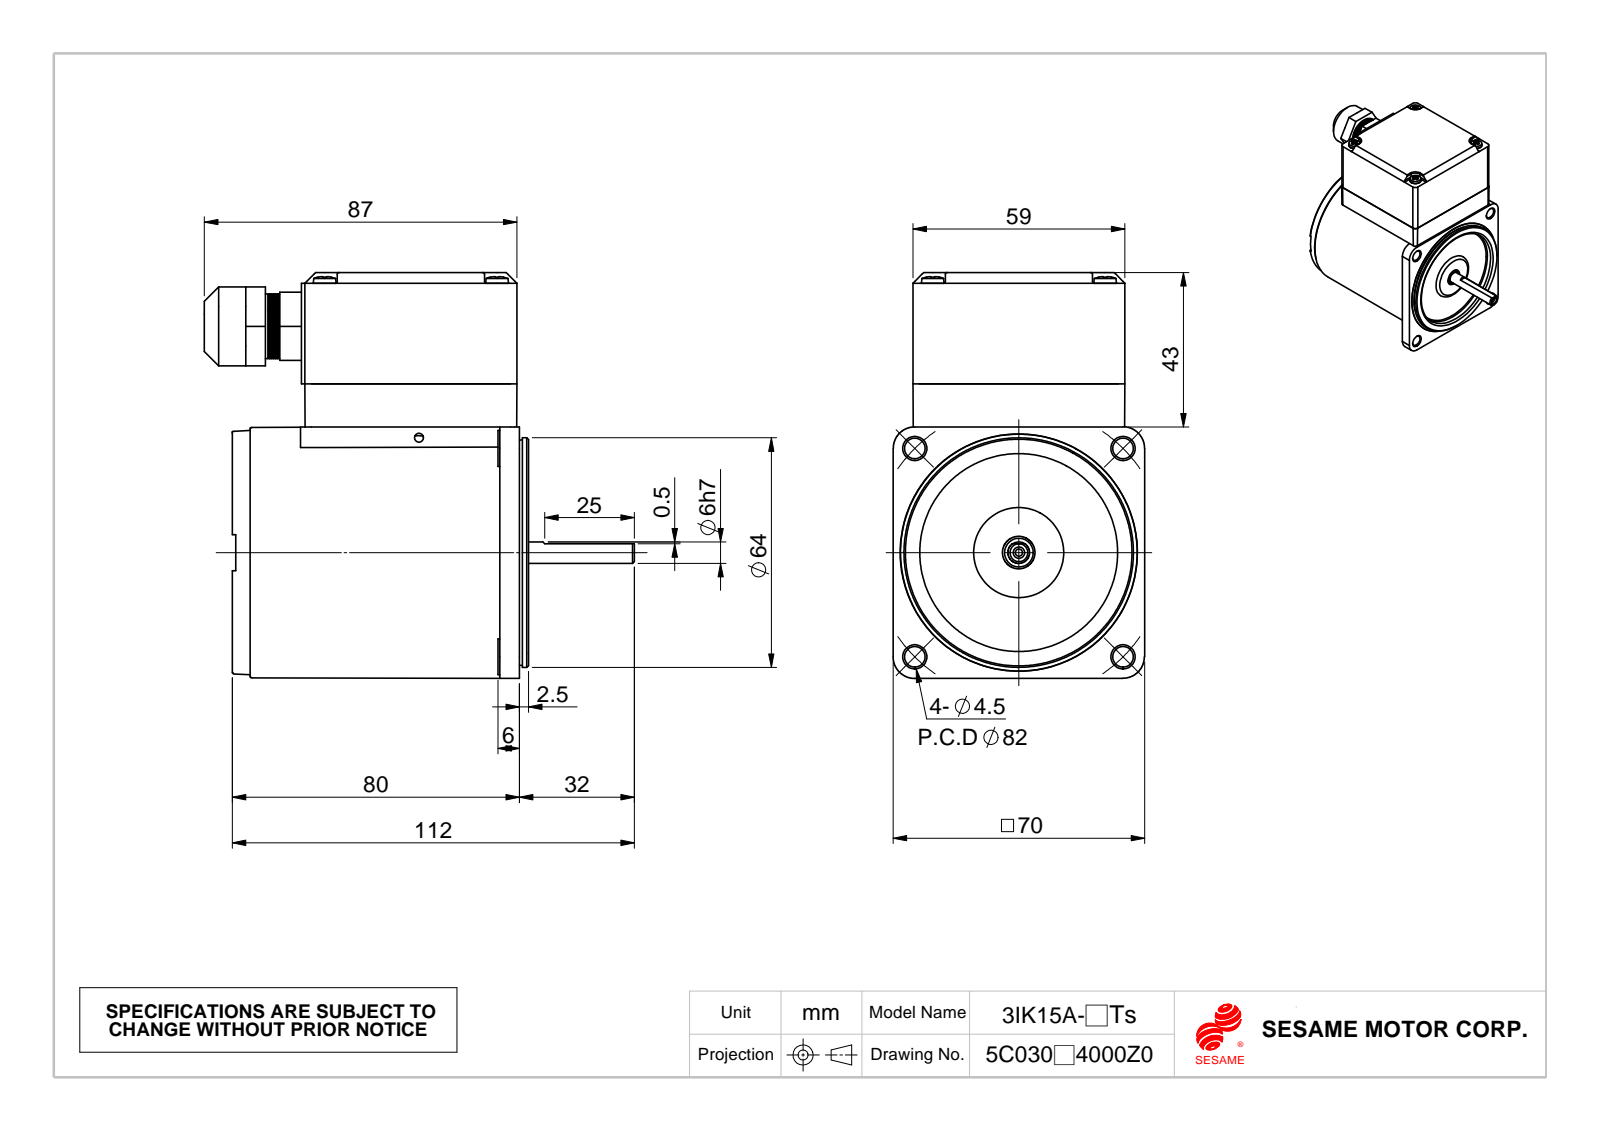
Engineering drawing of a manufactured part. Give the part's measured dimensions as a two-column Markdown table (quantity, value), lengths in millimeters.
| quantity | value |
| --- | --- |
| part name | 成品180度; M315Ts_2車工; C364_車工(成品); 15A_0.成品 (+1 more) |
| STEP written by | SolidWorks 2010 (CONFIG_CONTROL_DESIGN) |
| units | millimeters |
| bodies | 11 solids, 2391 faces (202 planar, 802 cylindrical, 1387 other) |
| overall size | 119.75 × 113 × 70 |
| volume | 468 940 mm³ |
| surface area | 72 882 mm² |
| round holes (diameter × count) | 3.3 × 4, 3.5 × 4, 3.9 × 4, 4.3 × 4, 5.75 × 4, 2 × 1, 2.5 × 1, 9 × 1, 11 × 1, 12 × 1, 14.5 × 1, 18 × 1 |
| round bosses / shafts (diameter × count) | 10 × 4, 6.3 × 4, 3 × 4, 63.93 × 1, 62.73 × 1, 57.42 × 1, 57.2 × 1, 22 × 1 |
| partial cylindrical surfaces (radius × count) | 2 × 12, 0.5 × 8, 4 × 6, 1.5 × 4, 3 × 4, 3.5 × 4, 6 × 4, 34.25 × 1 |
| main face-to-face distances | 12, 0.75, 77.4, 1.5, 77.5, 31, 43, 59, 75.89, 1.51 |
| hole center spacings | 41.01, 48, 58, 11.67, 12.35, 12.7, 24.93, 25 |
